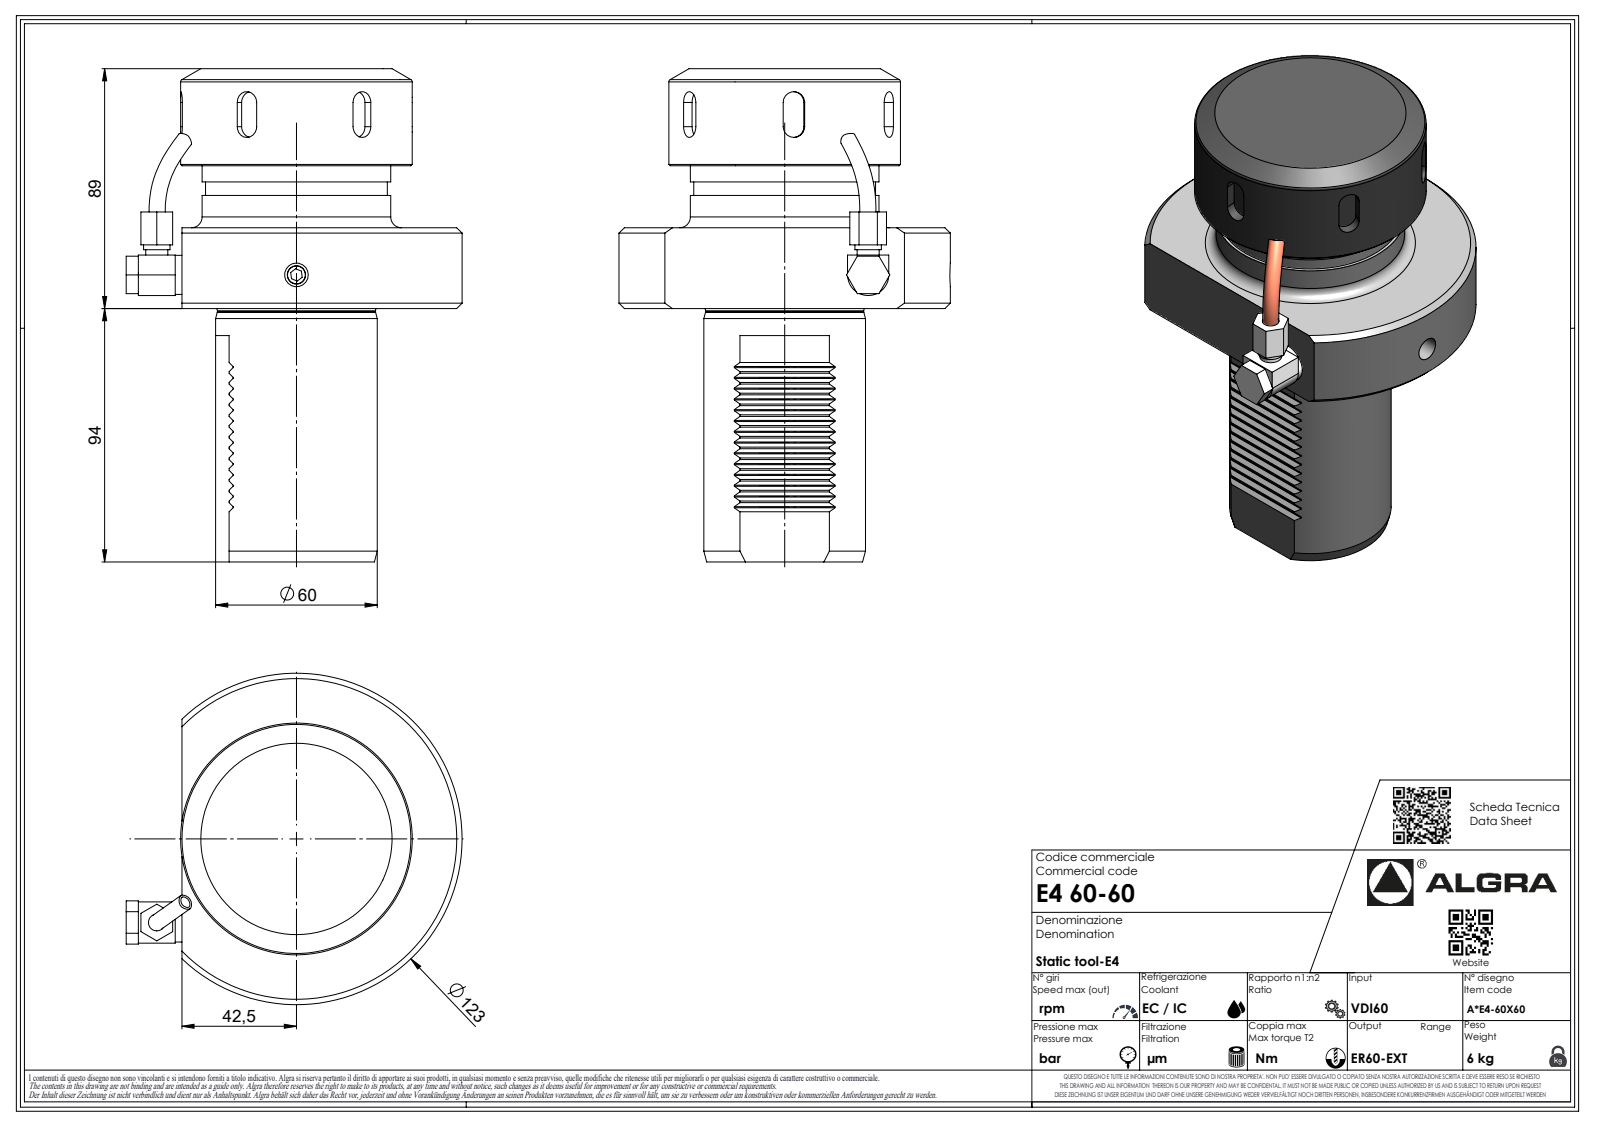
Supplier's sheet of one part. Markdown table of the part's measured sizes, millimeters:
| quantity | value |
| --- | --- |
| part name | E460-60 |
| STEP written by | SolidWorks 2023 (AUTOMOTIVE_DESIGN) |
| units | millimeters |
| bodies | 7 solids, 366 faces (243 planar, 68 cylindrical, 55 other) |
| overall size | 183 × 124.7 × 123 |
| volume | 1 146 000 mm³ |
| surface area | 130 002 mm² |
| round holes (diameter × count) | 6.8 × 2, 2.1 × 1 |
| round bosses / shafts (diameter × count) | 86 × 1, 70 × 1, 60 × 1, 58.7 × 1, 10 × 1, 9.8 × 1, 6.37 × 1, 1.7 × 1 |
| partial cylindrical surfaces (radius × count) | 0.3 × 14, 4 × 12, 0.33 × 7, 0.52 × 7, 3.7 × 7, 0.21 × 1, 7.65 × 1, 32.77 × 1 |
| main face-to-face distances | 30, 42, 47, 17, 12, 5, 20, 89, 59, 32 |
| hole center spacings | 46.54 |
